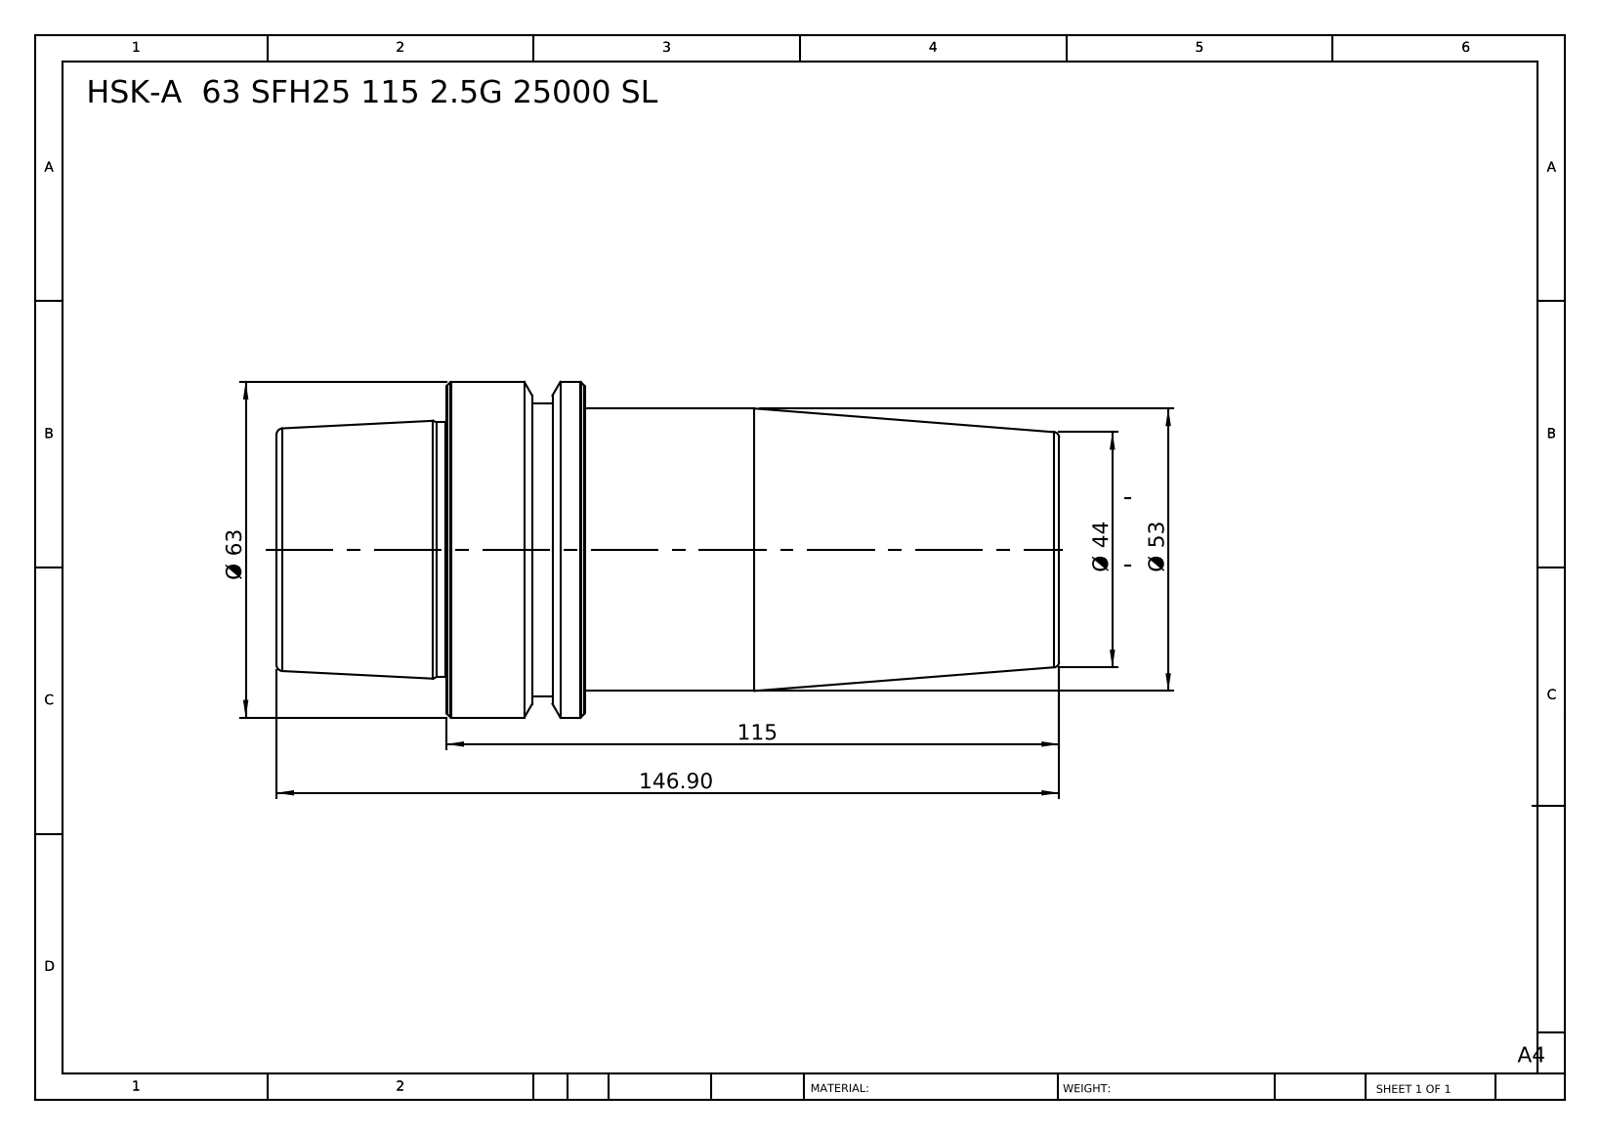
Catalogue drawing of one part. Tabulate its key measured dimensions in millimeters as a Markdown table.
| quantity | value |
| --- | --- |
| part name | HSK-A 63 SFH25 115 2.5G 25000 SL |
| STEP written by | SolidWorks 2014 (CONFIG_CONTROL_DESIGN) |
| units | millimeters |
| bodies | 1 solid, 46 faces (6 planar, 10 cylindrical, 30 other) |
| overall size | 146.9 × 63 × 63 |
| volume | 308 714 mm³ |
| surface area | 29 951 mm² |
| round bosses / shafts (diameter × count) | 63 × 1, 55 × 1, 53 × 1, 47.78 × 1 |
| main face-to-face distances | 146.9, 89, 57.9, 115, 26, 31.9, 95.1, 6.1, 19.9, 51.8 |
